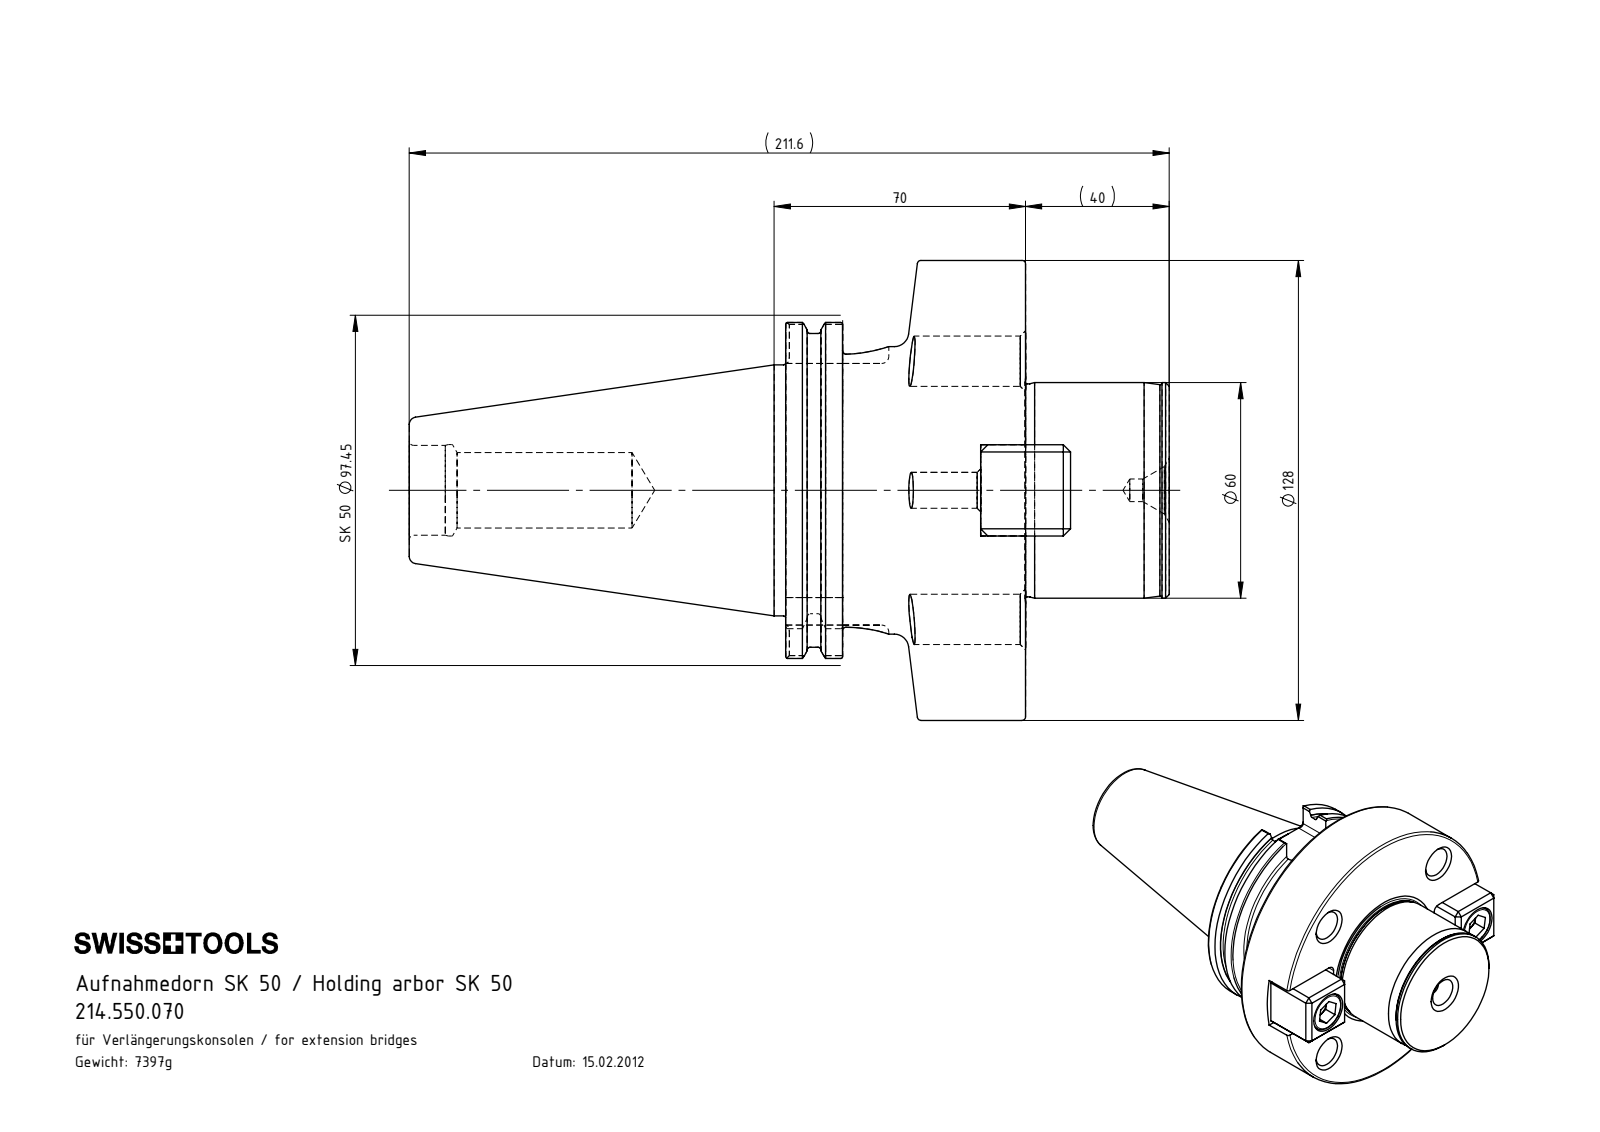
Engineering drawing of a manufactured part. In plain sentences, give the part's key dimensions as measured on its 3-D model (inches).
The part is named "U00-D60.ER1.025; ISO 4762 - M12 x 25_PreviewCfg; 214.550.070; SK5-D60.K01.070". Its 3-D file was written by "SolidWorks 2022 (CONFIG_CONTROL_DESIGN)". It is 5 solids with 292 faces: 113 planar, 74 cylindrical and 105 other. Overall it measures 8.331 by 5.039 by 5.039 inches. Its volume is 57.51 cubic inches and its surface area 154.2 square inches. Round holes: 4 of diameter 0.551, 2 of diameter 0.394, 2 of diameter 0.512, 2 of diameter 0.748, 1 of diameter 0.248, 1 of diameter 0.827, 1 of diameter 0.984, 1 of diameter 1.002. Round bosses or shafts: 2 of diameter 0.709, 2 of diameter 0.472, 1 of diameter 5.039, 1 of diameter 3.583, 1 of diameter 3.15, 1 of diameter 2.75, 1 of diameter 2.362, 1 of diameter 2.335. Partial cylindrical surfaces (rounded edges, fillets, slot ends): 8 of radius 0.079, 4 of radius 0.118, 1 of radius 0.506, 1 of radius 1.919. The main face-to-face distances are 2.63, 1, 0.492, 4.205, 1.575, 2.138, 2.067, 0.624, 1.514, 2.006. The hole center spacings are 1.505, 2, 2.828, 3.63, 1.929, 4, 3.858.
